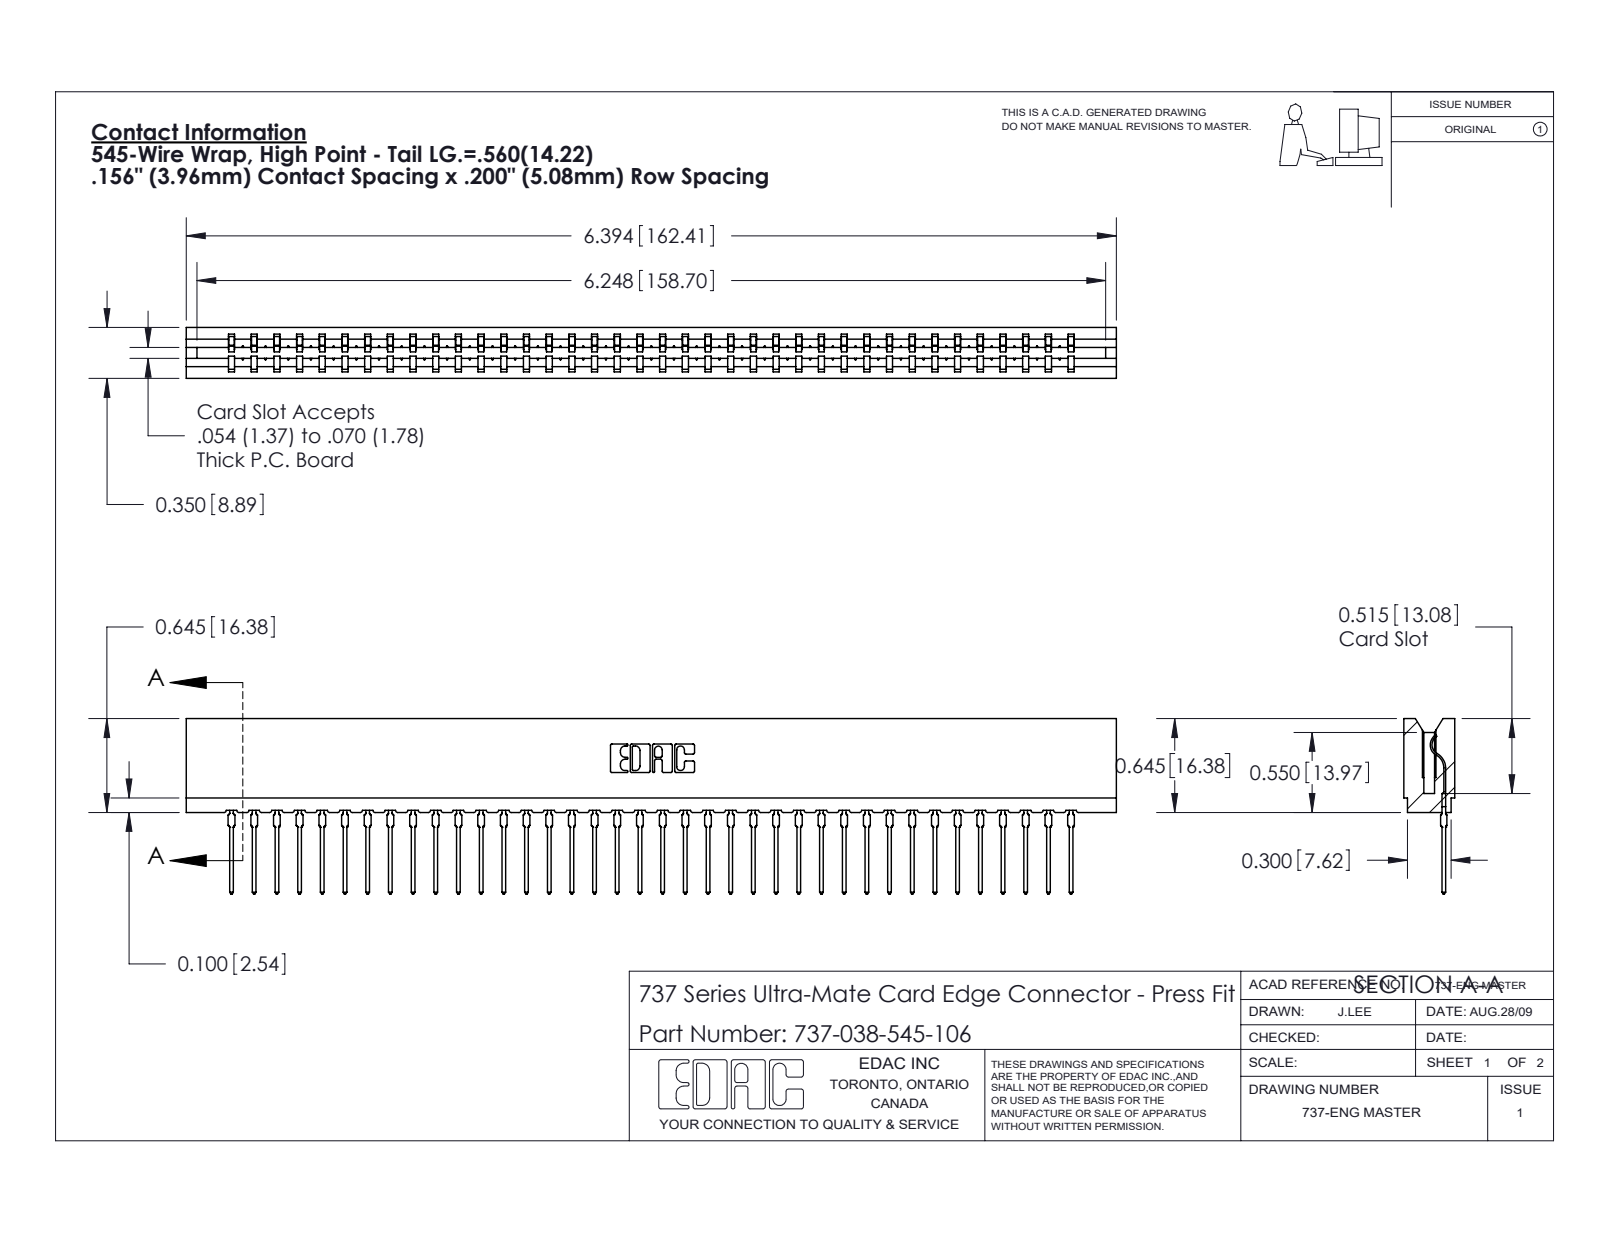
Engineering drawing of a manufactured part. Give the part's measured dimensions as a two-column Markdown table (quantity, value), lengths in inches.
| quantity | value |
| --- | --- |
| part name | 737 Part_Insulator Option - 06; 745-292-001_545; 737-038-545-106 |
| STEP written by | SolidWorks 2020 (CONFIG_CONTROL_DESIGN) |
| units | inches |
| bodies | 39 solids, 4389 faces (2639 planar, 762 cylindrical, 988 other) |
| overall size | 6.394 × 1.206 × 0.35 |
| volume | 0.965 in³ |
| surface area | 33.79 in² |
| partial cylindrical surfaces (radius × count) | 0.015 × 76, 0.021 × 76, 0.01 × 22, 0.007 × 6, 0.031 × 6, 0.005 × 4, 0.011 × 4, 0.026 × 3 |
| main face-to-face distances | 0.138, 0.212, 0.35, 0.074, 0.045, 0.305, 0.093, 0.167, 0.063, 0.287 |
